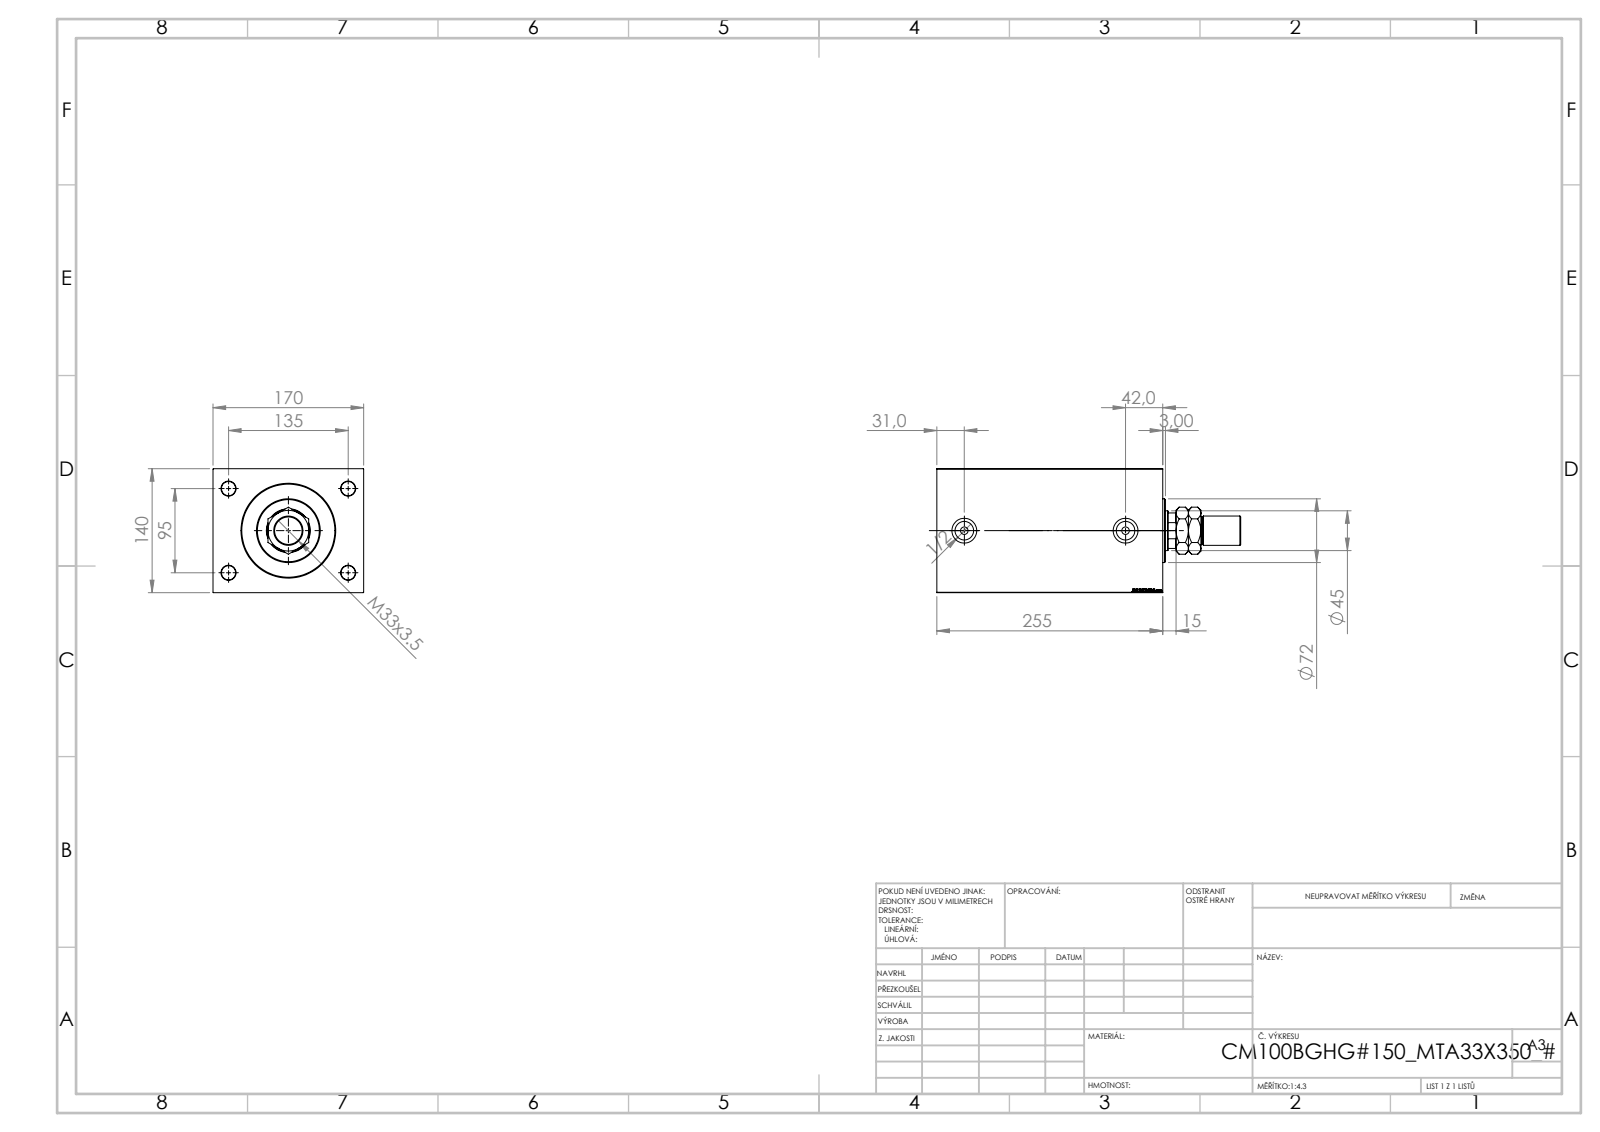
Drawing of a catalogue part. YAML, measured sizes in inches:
part_name: "V450CM_B_VCP; V450CM_B_Body; V450CM_VC_B; MTA"
step_written_by: "SolidWorks 2019 (CONFIG_CONTROL_DESIGN)"
units: inches
bodies: {solids: 4, faces: 933, planar: 417, cylindrical: 60, other: 456}
overall_size: [13.504, 6.693, 5.512]
volume: 314.5
surface_area: 607.8
round_holes:
  - {diameter: 0.63, count: 4}
  - {diameter: 0.335, count: 2}
  - {diameter: 0.825, count: 2}
  - {diameter: 1.102, count: 2}
  - {diameter: 1.24, count: 1}
  - {diameter: 1.772, count: 1}
  - {diameter: 1.909, count: 1}
  - {diameter: 1.949, count: 1}
  - {diameter: 3.937, count: 1}
  - {diameter: 4.016, count: 1}
  - {diameter: 4.134, count: 1}
round_bosses_or_shafts:
  - {diameter: 2.835, count: 1}
  - {diameter: 1.299, count: 1}
  - {diameter: 1.22, count: 1}
partial_cylinders:
  - {radius: 0.866, count: 1}
face_to_face_distances: [5.512, 6.693, 10.039, 9.016, 1.024, 0.591, 8.425, 9.449, 3.543, 2.52]
hole_center_spacings: [3.25, 3.74, 5.315, 6.499, 7.165]
